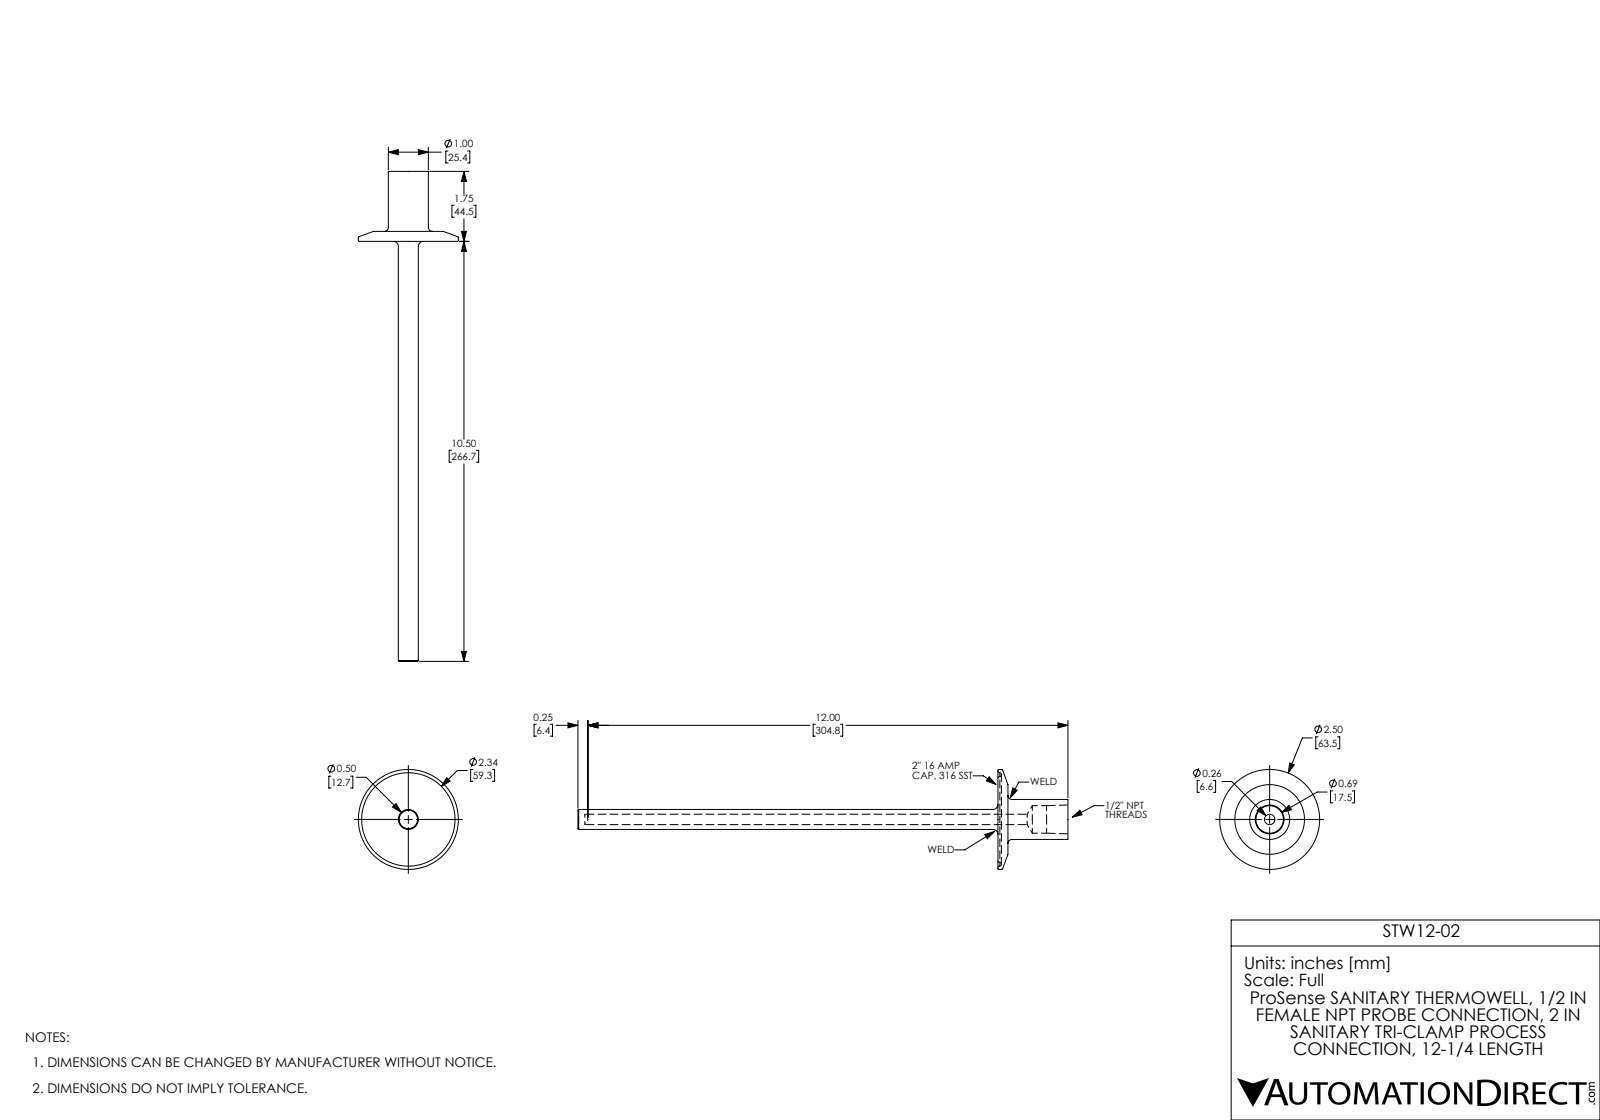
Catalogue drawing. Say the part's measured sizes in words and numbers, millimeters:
The part is named "STW12-02". Its 3-D file was written by "SolidWorks 2017 (AUTOMOTIVE_DESIGN)". It is 1 solid with 45 faces: 5 planar, 10 cylindrical and 30 other. Overall it measures 311.2 by 63.5 by 63.5 millimeters. Its volume is 53 850 cubic millimeters and its surface area 28 010 square millimeters. Round holes: 1 of diameter 6.6, 1 of diameter 17.5. Round bosses or shafts: 1 of diameter 63.5, 1 of diameter 25.4, 1 of diameter 12.7. The main face-to-face distances are 6.4, 38.1, 44.5, 311.2, 273.1, 266.7.
